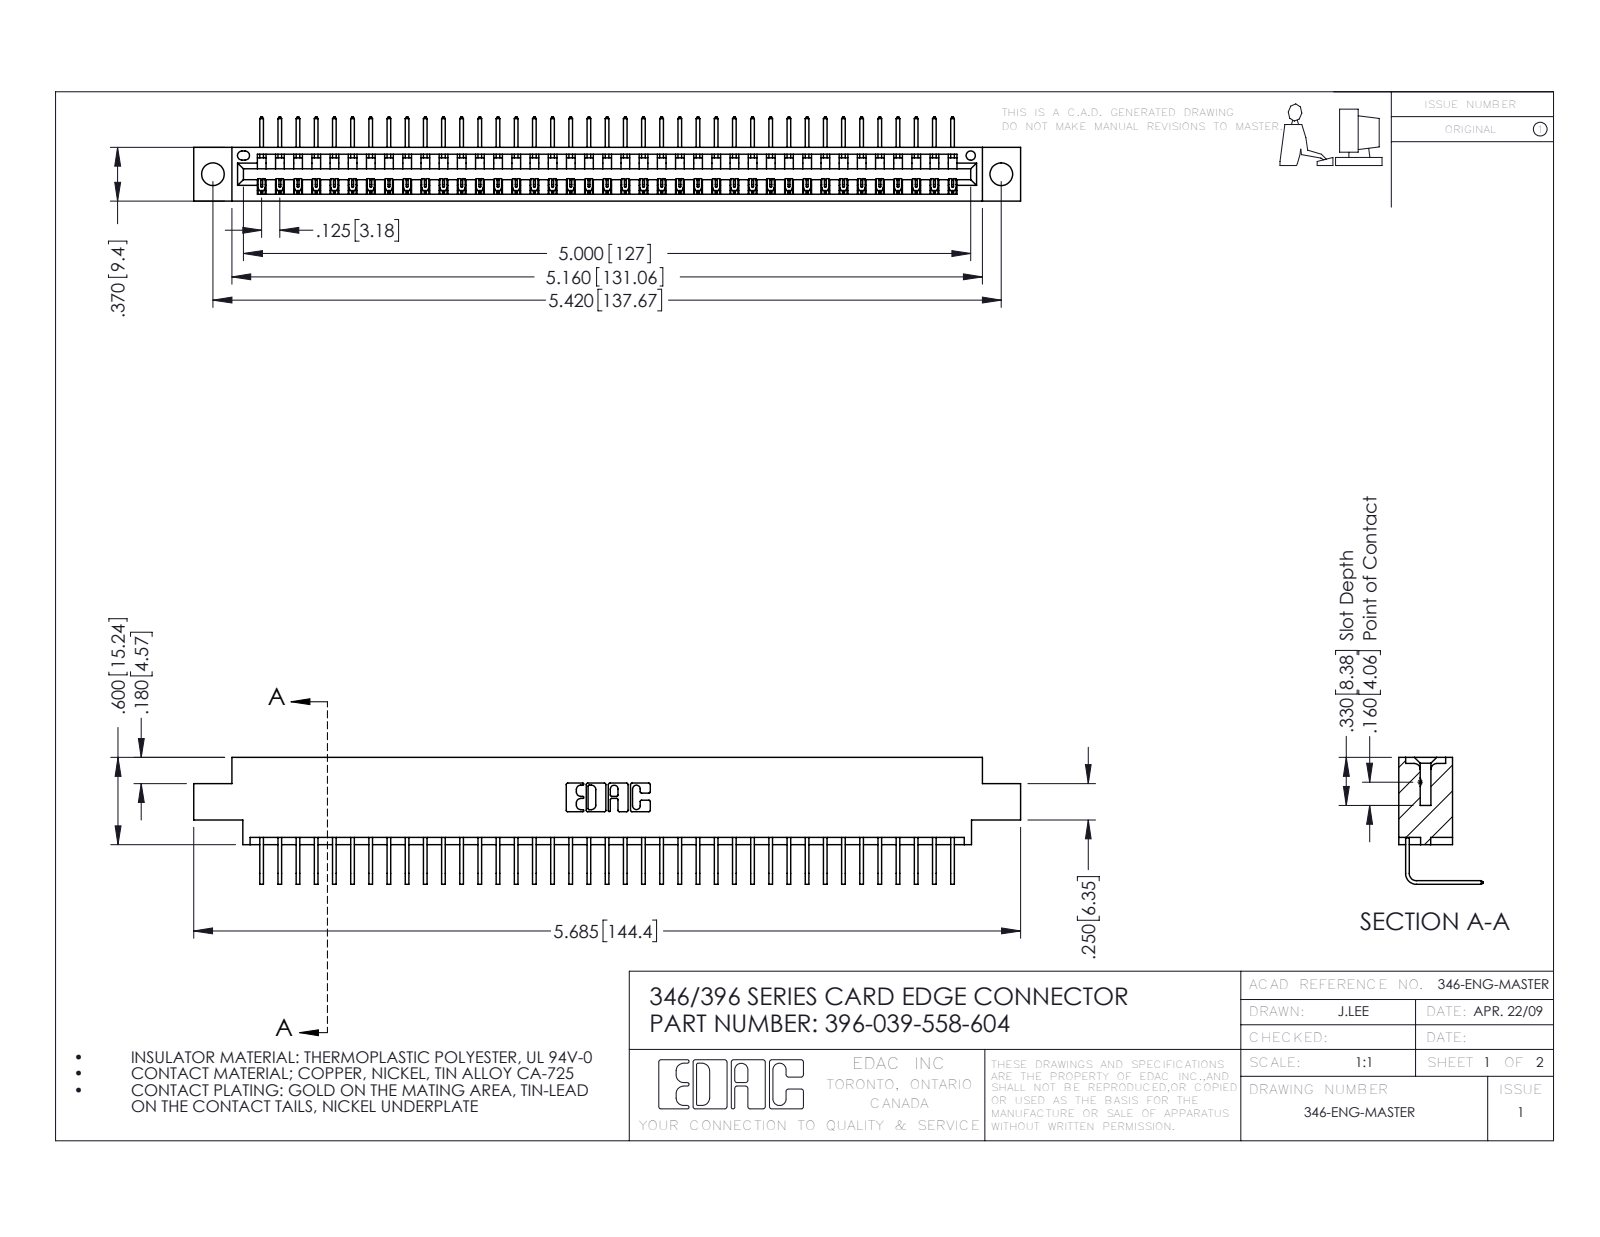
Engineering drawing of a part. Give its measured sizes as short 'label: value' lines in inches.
name: 396-039-558-604; 346 Part_0.170 Offset - 0.156 Dia-TH; 345-292-001_558 Tail - 2
written by: SolidWorks 2016 (CONFIG_CONTROL_DESIGN)
unit: in
bodies: 40 solids, 2466 faces (1718 planar, 748 cylindrical, 0 other)
size: 5.685 × 0.873 × 0.58
volume: 0.835 in³; area: 27.62 in²
holes: 2× ⌀0.156, 1× ⌀0.064
rounds: 78× R0.006, 22× R0.01, 6× R0.007, 6× R0.031, 3× R0.026, 2× R0.031, 2× R0.04, 1× R0.014
face distances: 0.322, 0.048, 0.37, 0.25, 0.298, 0.025, 0.072, 0.148, 0.222, 0.1
hole spacings: 0.246, 5.211, 5.42
